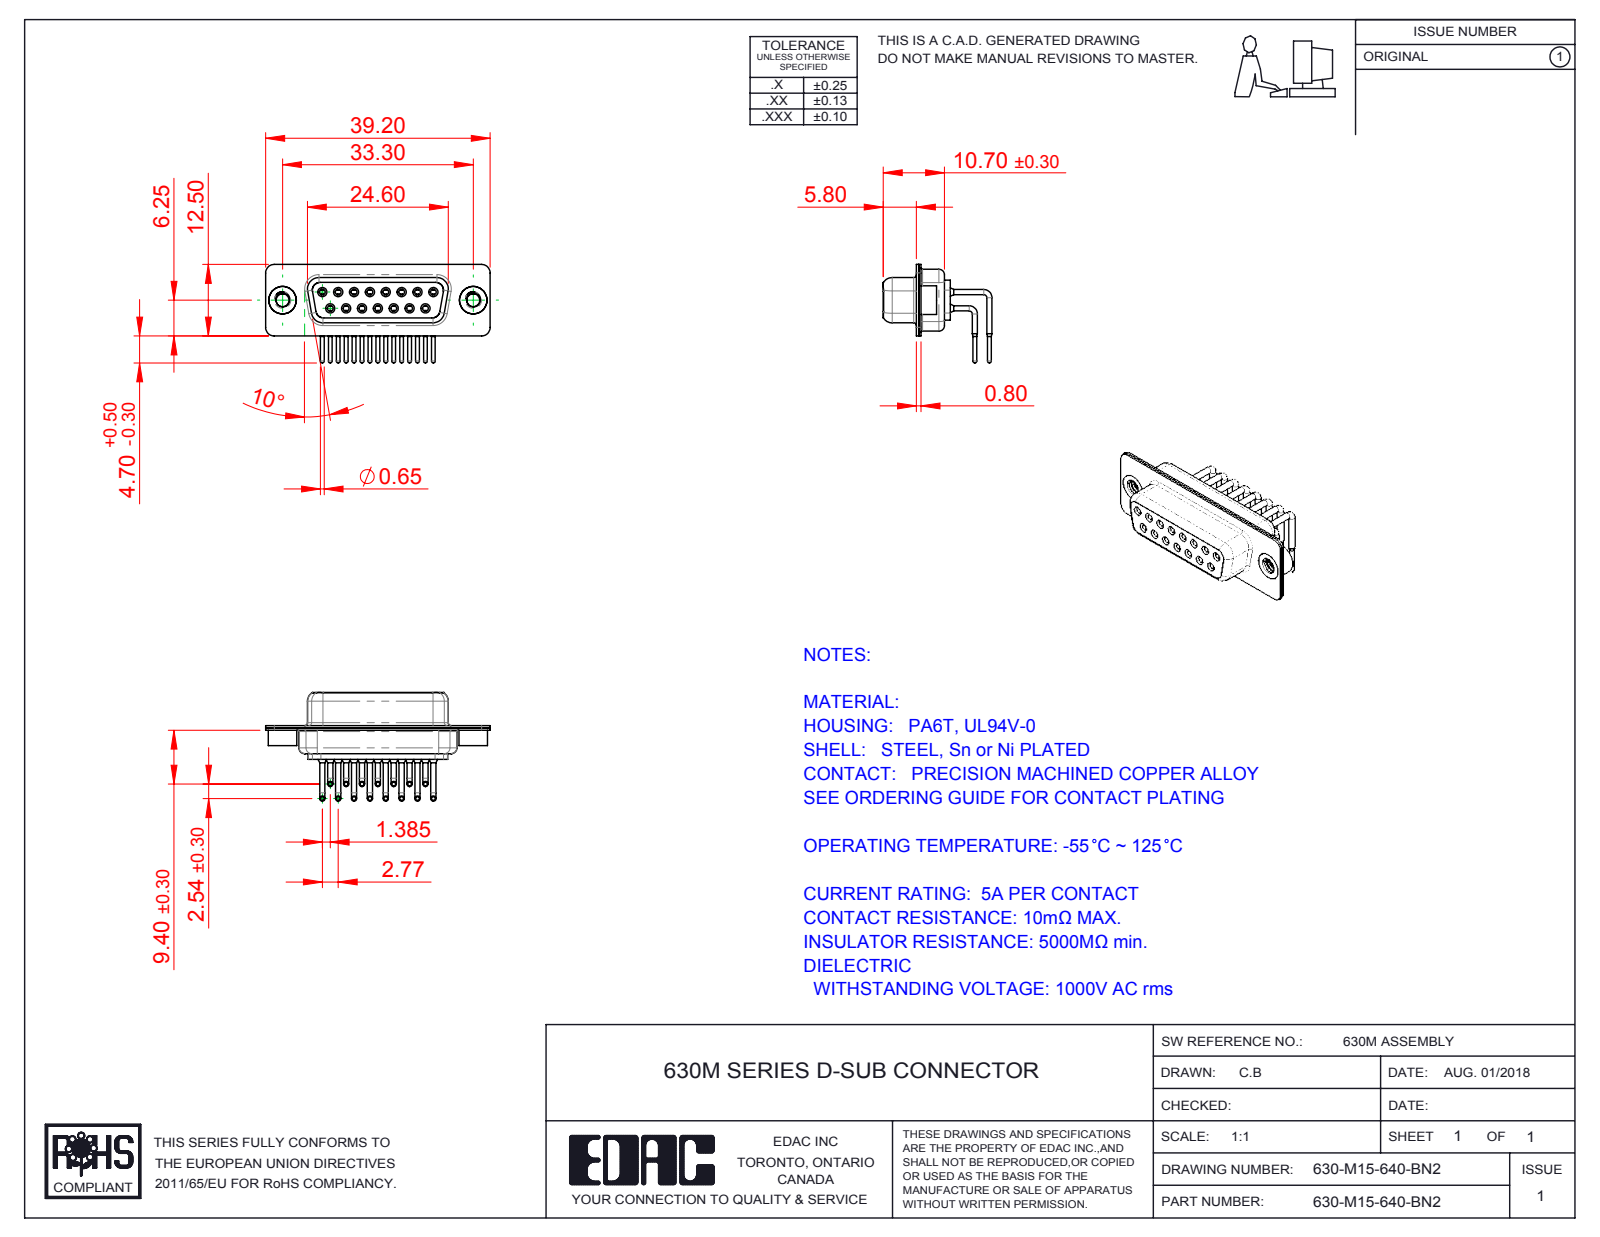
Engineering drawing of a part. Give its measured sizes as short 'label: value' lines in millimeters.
name: 630-M15-640-BN2; 630M Housing_15 Contacts; 630M Contact Row 1; 630M Shell Rear_15 Contacts (+3 more)
written by: SolidWorks 2016 (CONFIG_CONTROL_DESIGN)
unit: mm
bodies: 20 solids, 1074 faces (292 planar, 482 cylindrical, 300 other)
size: 39.2 × 18.99 × 17.2
volume: 2 568 mm³; area: 6 554 mm²
holes: 15× ⌀1, 15× ⌀1.1, 15× ⌀1.7, 15× ⌀1.8, 15× ⌀2, 2× ⌀2.26, 2× ⌀4, 2× ⌀4.8
bosses: 30× ⌀0.9, 15× ⌀1.6, 15× ⌀1.5, 15× ⌀0.65, 2× ⌀5, 2× ⌀4.9
rounds: 16× R1.5, 12× R2, 8× R1.35, 8× R1.6, 4× R0.25, 4× R0.5, 4× R0.6, 4× R0.65
face distances: 0.4, 1.45, 8.95, 2.3, 6.2, 0.8, 1.9, 8.5, 0.45, 7.05
hole spacings: 3.16, 2.77, 5.54, 8.31, 11.08, 5.03, 5.04, 7.48
